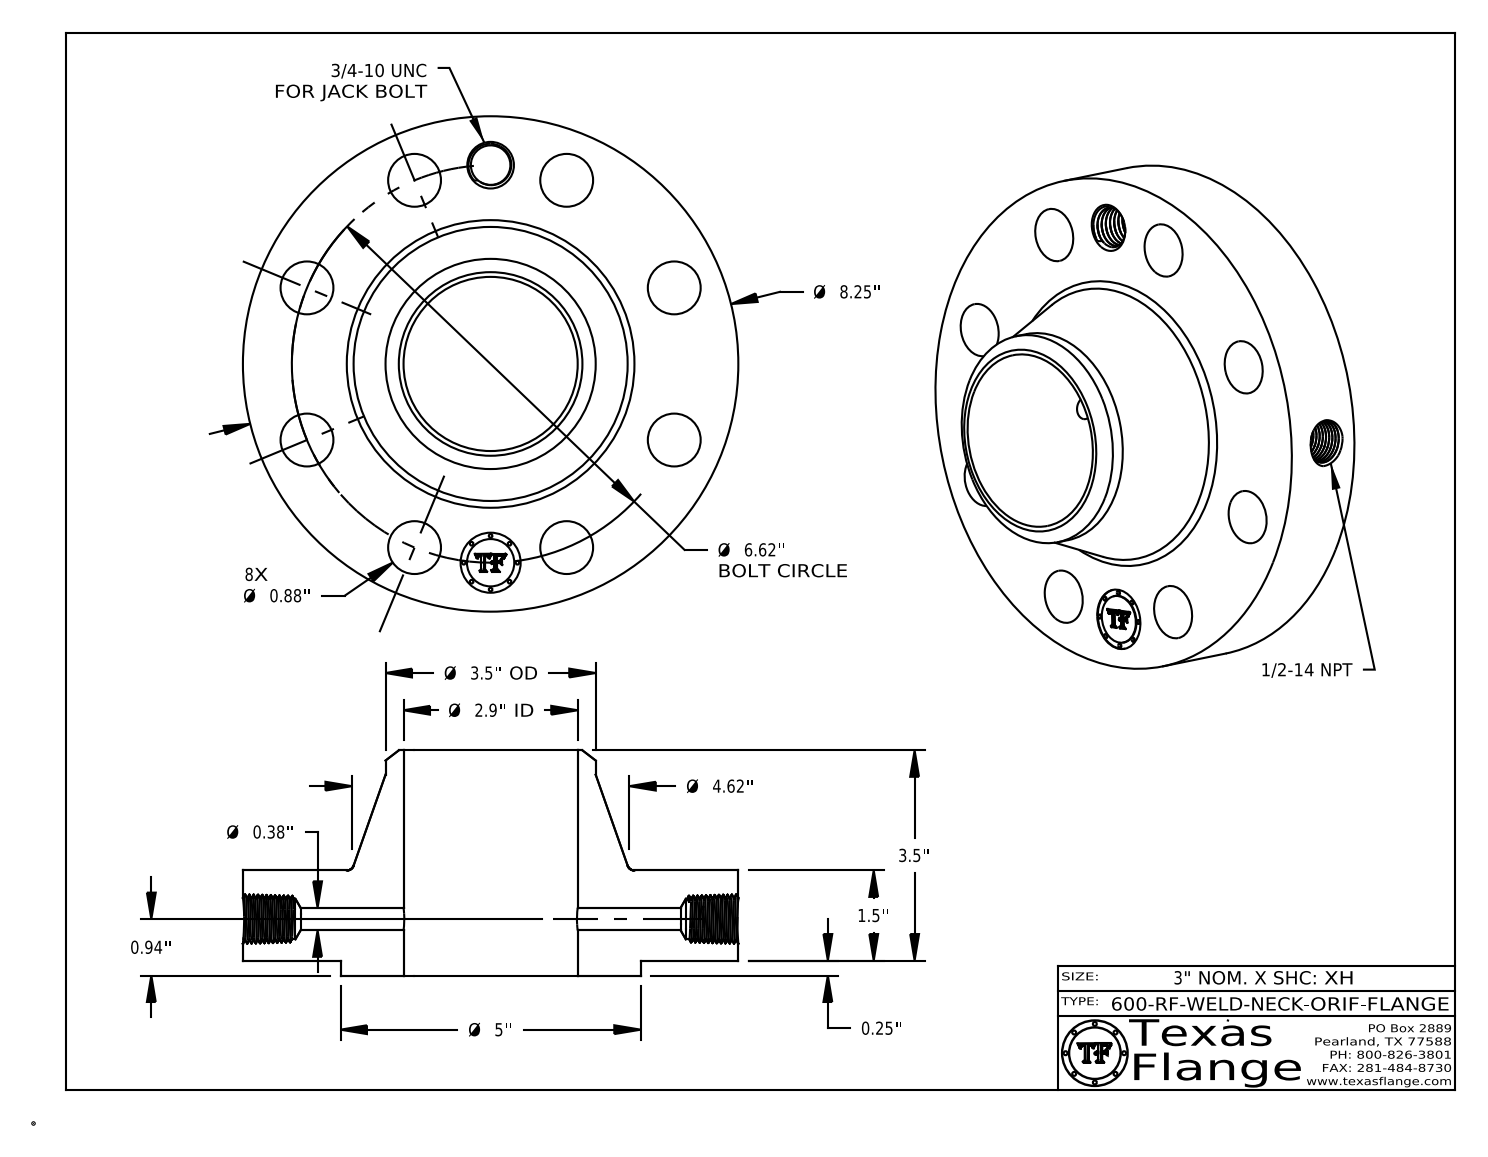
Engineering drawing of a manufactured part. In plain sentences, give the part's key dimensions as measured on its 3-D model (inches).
The part is named "600-RF-WELD-NECK". Its 3-D file was written by "CATIA V5 STEP AP214 (AUTOMOTIVE_DESIGN)". It is 1 solid with 769 faces: 369 planar, 92 cylindrical and 308 other. Overall it measures 8.25 by 8.25 by 3.75 inches. Its volume is 75.78 cubic inches and its surface area 225.9 square inches. Round holes: 8 of diameter 0.88, 1 of diameter 0.375, 1 of diameter 0.656, 1 of diameter 0.672, 1 of diameter 1, 1 of diameter 2.9. Round bosses or shafts: 8 of diameter 0.061, 1 of diameter 8.25, 1 of diameter 5, 1 of diameter 3.5, 1 of diameter 0.788. The main face-to-face distances are 1.5, 0.25, 1.75, 3.75, 3.5, 2, 0.015, 1.735, 1.485, 2.015. The hole center spacings are 3.31, 4.681, 6.116, 6.62, 1.291, 2.533, 2.533, 3.678.
